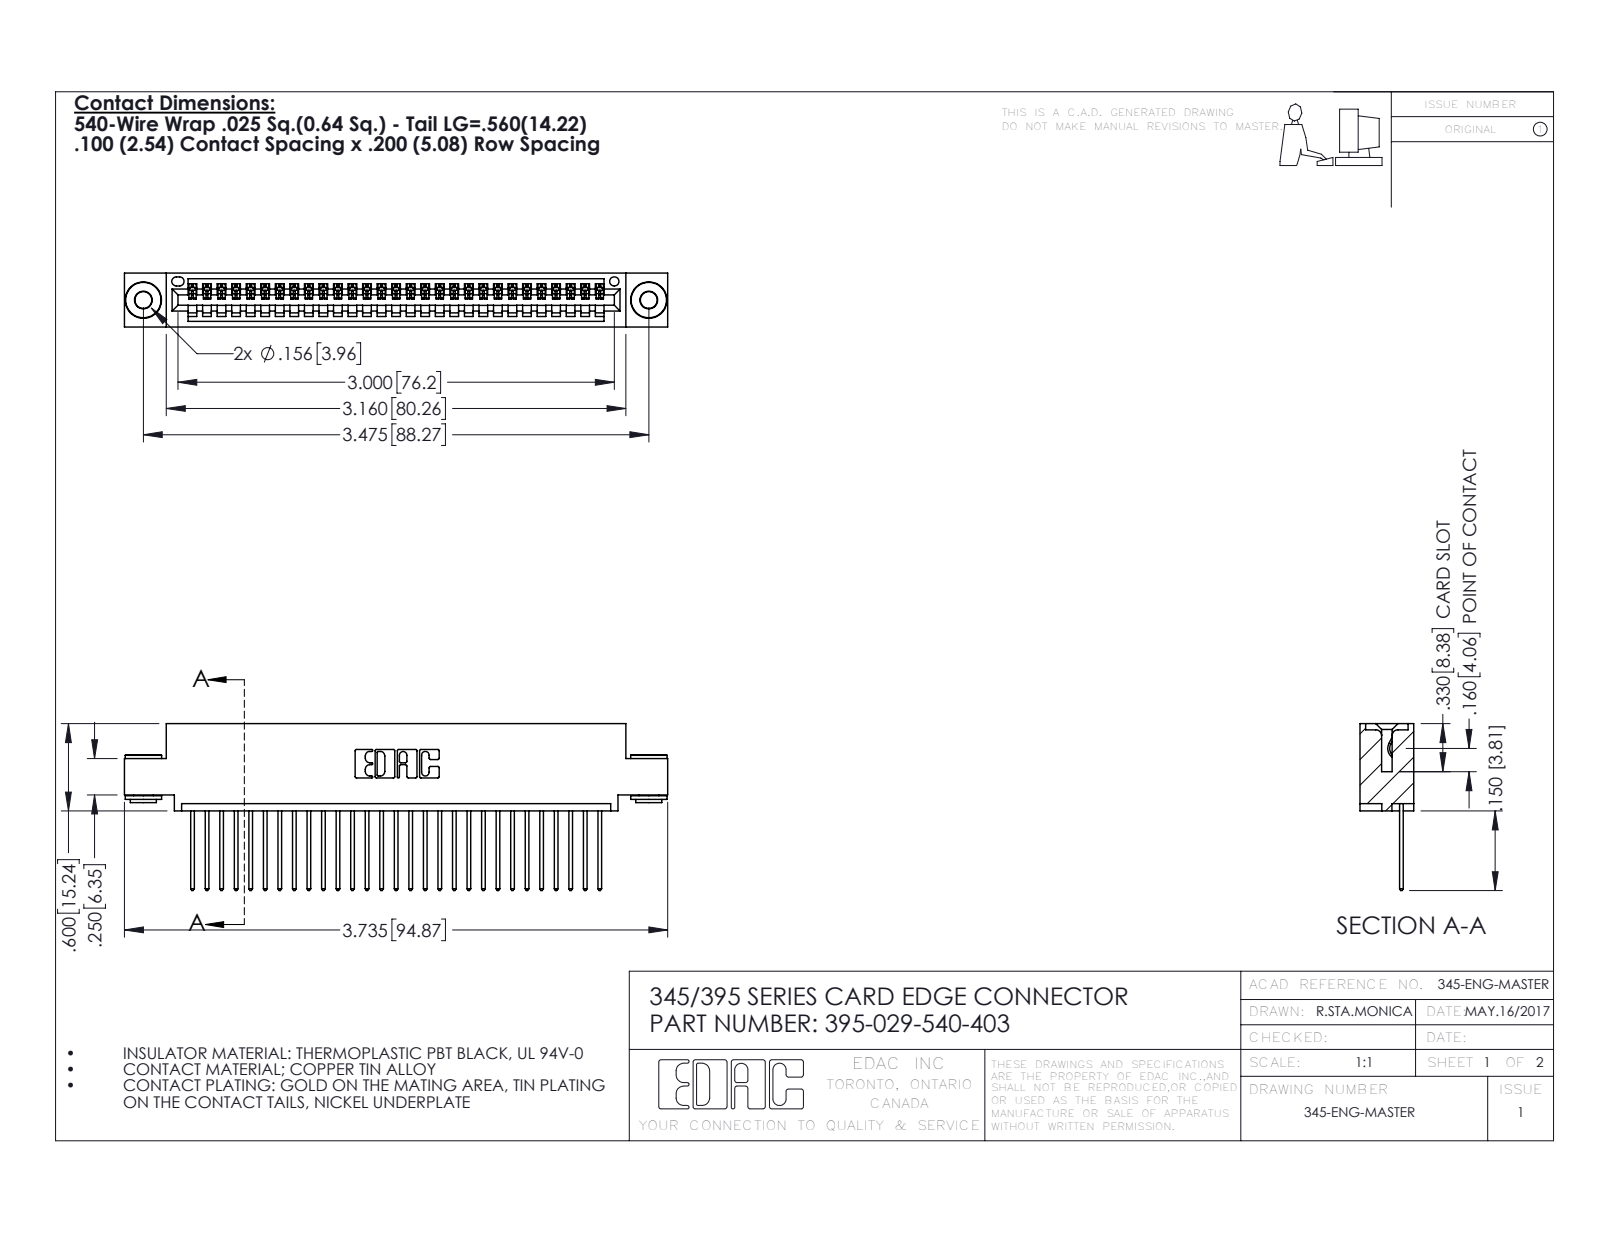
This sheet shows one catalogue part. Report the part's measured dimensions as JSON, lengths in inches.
{"part_name": "345-292-001_345-293-140; 395-029-540-403; 345 Part_0.110 Offset - 0.156 Dia-TH; 345-250-002_345-250-002-102", "step_written_by": "SolidWorks 2016 (CONFIG_CONTROL_DESIGN)", "units": "inches", "bodies": {"solids": 32, "faces": 1850, "planar": 1254, "cylindrical": 588, "other": 8}, "overall_size": [3.735, 1.147, 0.37], "volume_in3": 0.542, "surface_area_in2": 18.93, "round_holes": [[0.116, 2], [0.156, 2], [0.064, 1]], "round_bosses_or_shafts": [[0.25, 2], [0.18, 2], [0.136, 2]], "partial_cylinders_radius": [[0.006, 58], [0.01, 58], [0.01, 22], [0.007, 6], [0.031, 6], [0.026, 3], [0.031, 2], [0.04, 2]], "face_to_face_distances": [0.072, 0.298, 0.37, 0.025, 0.2, 0.098, 0.272, 0.225, 0.149, 0.072], "hole_center_spacings": [0.27, 3.24, 3.475]}
